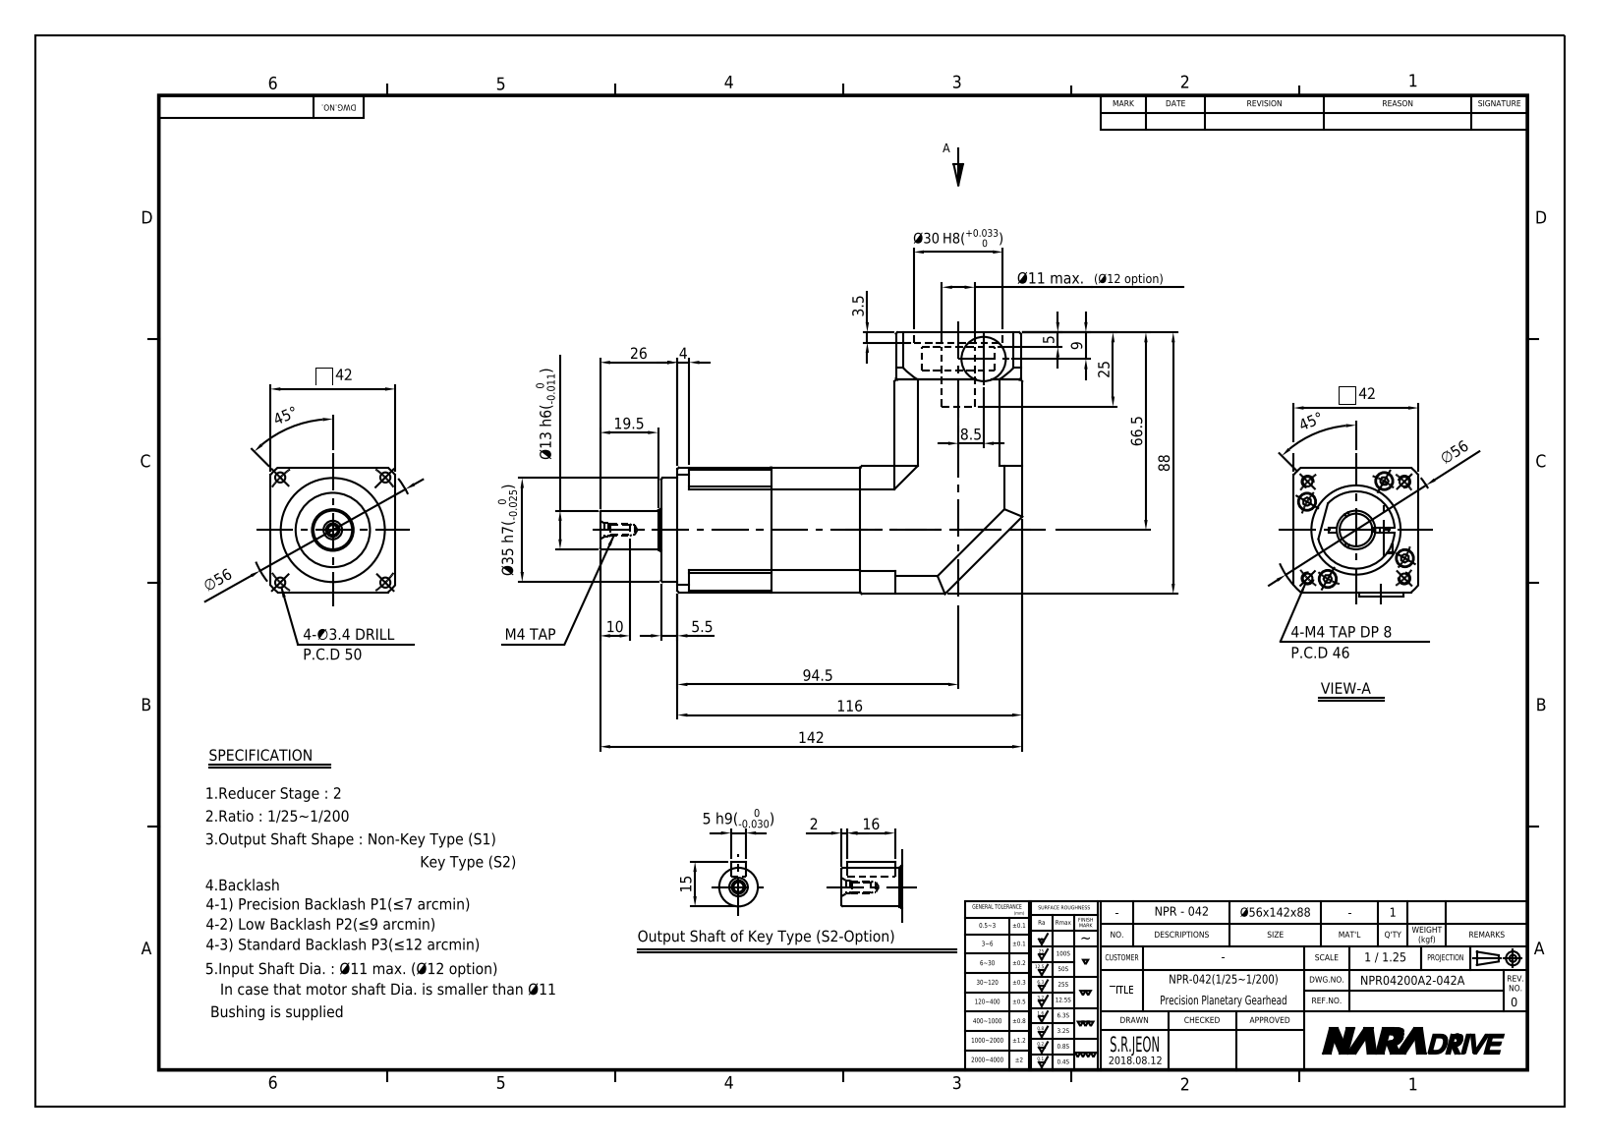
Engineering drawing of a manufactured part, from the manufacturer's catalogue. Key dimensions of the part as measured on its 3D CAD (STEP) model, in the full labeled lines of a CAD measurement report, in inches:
Part name (STEP PRODUCT): NPR04200A2-042A-S1
STEP written by: Autodesk Inventor 2015 (AUTOMOTIVE_DESIGN)
Units: inches
Bodies: 2 solids, 407 faces (205 planar, 102 cylindrical, 100 other)
Overall size (bounding box): 5.591 × 3.465 × 1.732
Volume: 13.51 in³ · Surface area: 75.65 in²
Round holes (diameter × count): ⌀0.134 ×15, ⌀0.097 ×9, ⌀0.236 ×8, ⌀0.128 ×5, ⌀1.181 ×2, ⌀0.177 ×1, ⌀0.276 ×1, ⌀0.335 ×1, ⌀0.433 ×1, ⌀0.512 ×1, ⌀1.102 ×1, ⌀1.26 ×1
Round bosses / shafts (diameter × count): ⌀0.217 ×9, ⌀0.118 ×9, ⌀1.378 ×1, ⌀1.024 ×1, ⌀0.984 ×1, ⌀0.591 ×1, ⌀0.551 ×1, ⌀0.512 ×1
Partial cylindrical surfaces — rounded edges, fillets, slot ends (radius × count): R0.197 ×4, R1.004 ×2, R1.102 ×2, R0.118 ×1, R0.984 ×1
Main face-to-face distances: 0.02, 1.673, 1.654, 1.693, 1.988, 1.575, 0.315, 0.846, 0.217, 2.618
Hole centre spacings: 0.817, 1.129, 0.263, 0.748, 0.906, 0.984, 1.155, 1.639
